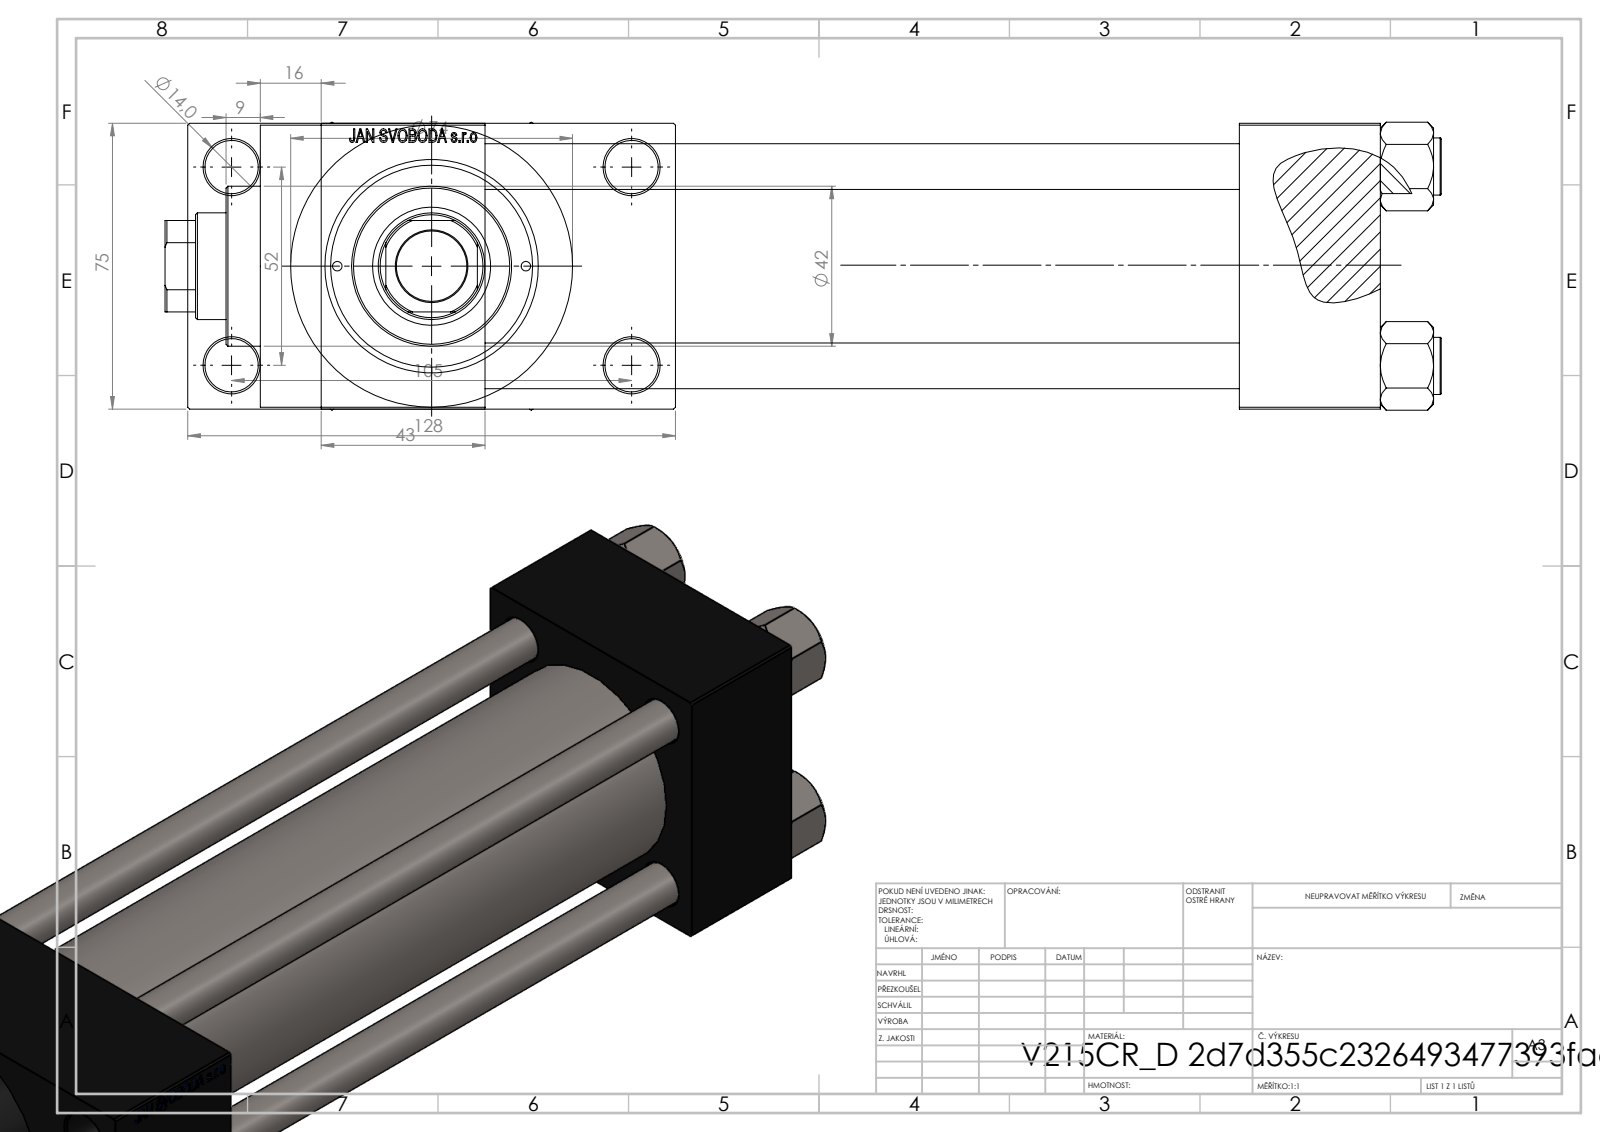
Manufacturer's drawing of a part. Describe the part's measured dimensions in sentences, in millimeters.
The part is named "V215CR_D_TYCINKA; V215CR_D_Body; V215_VC_A; NUT_M5_D (+1 more)". Its 3-D file was written by "SolidWorks 2019 (CONFIG_CONTROL_DESIGN)". It is 11 solids with 1112 faces: 499 planar, 93 cylindrical and 520 other. Overall it measures 335 by 128 by 75.54 millimeters. Its volume is 1 034 000 cubic millimeters and its surface area 248 847 square millimeters. Round holes: 4 of diameter 12, 4 of diameter 14, 2 of diameter 2.5, 2 of diameter 7, 2 of diameter 20.96, 2 of diameter 30, 1 of diameter 18.5, 1 of diameter 28, 1 of diameter 31, 1 of diameter 41, 1 of diameter 50, 1 of diameter 53. Round bosses or shafts: 4 of diameter 15, 1 of diameter 74, 1 of diameter 56, 1 of diameter 42. Partial cylindrical surfaces (rounded edges, fillets, slot ends): 1 of radius 13.5. The main face-to-face distances are 75, 198, 37, 235, 26.5, 101.5, 278, 241, 43, 16. The hole center spacings are 26.19, 26.35, 36.98, 38.03, 52.3, 57.22, 58.43, 58.59.
